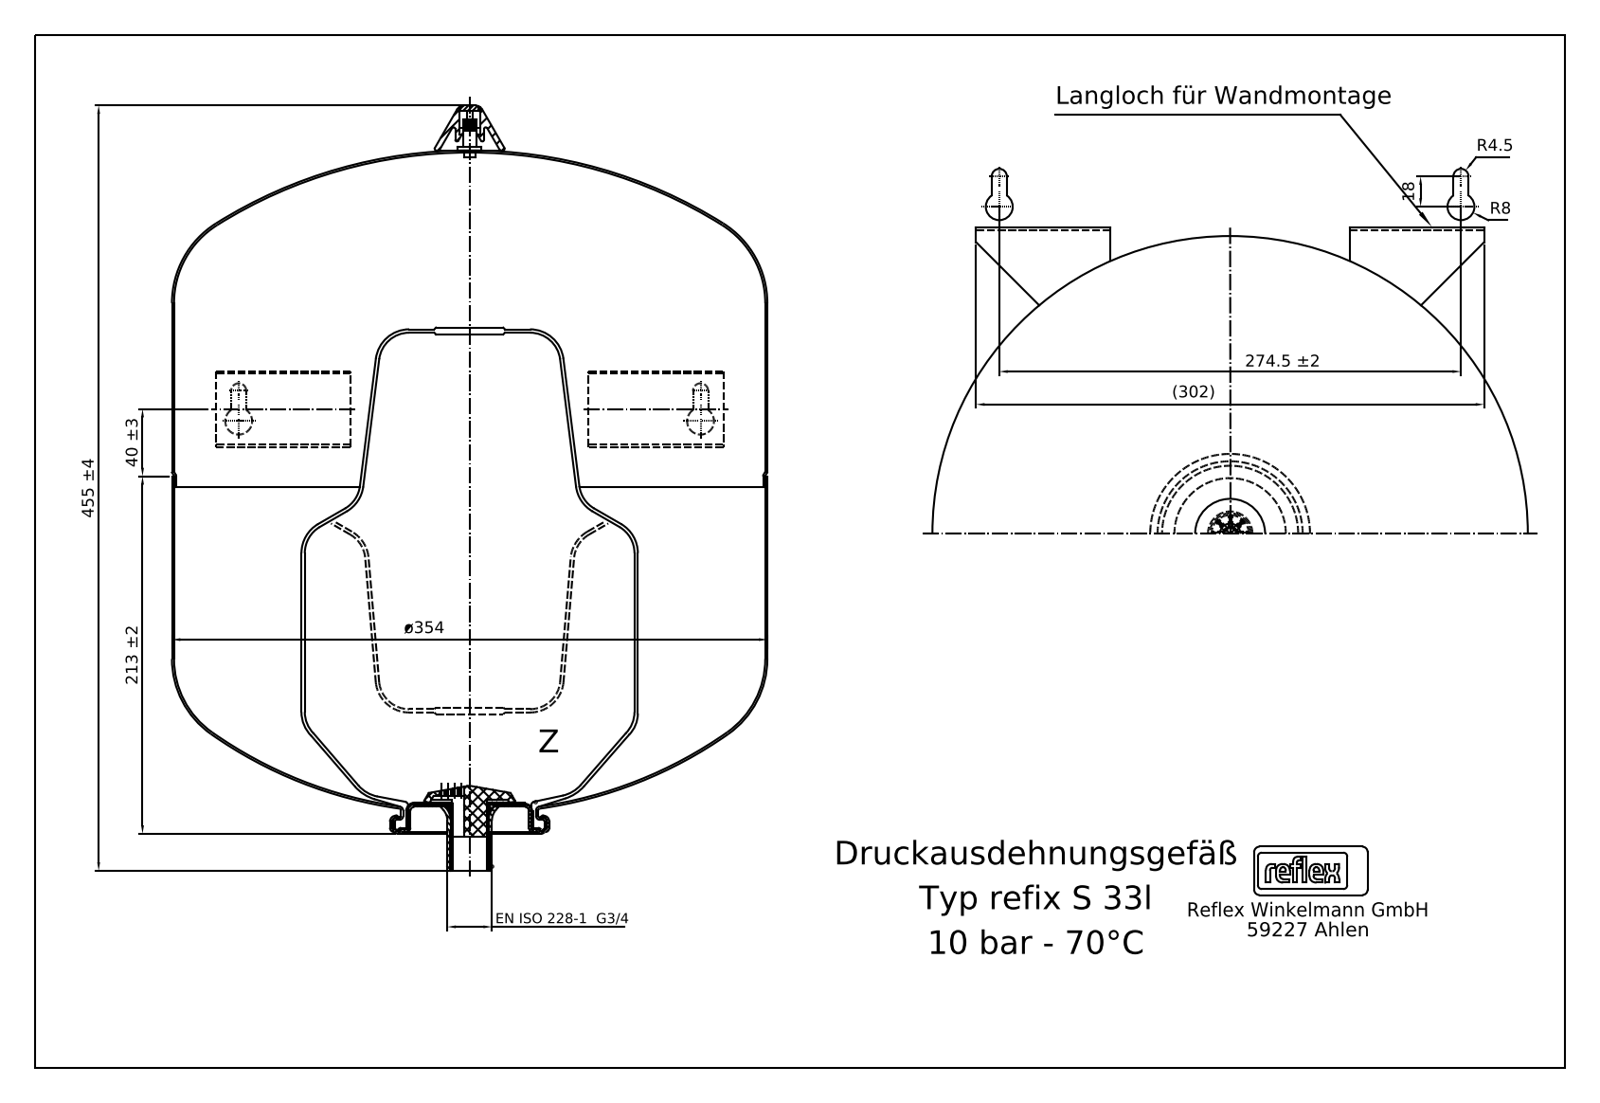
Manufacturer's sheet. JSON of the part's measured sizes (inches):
{"step_written_by": "Mechanical Desktop 2011 (CONFIG_CONTROL_DESIGN)", "units": "inches", "bodies": {"solids": 16, "faces": 276, "planar": 124, "cylindrical": 102, "other": 50}, "overall_size": [17.913, 14.185, 13.937], "volume_in3": 1967, "surface_area_in2": 1512, "round_holes": [[0.555, 1], [0.63, 1], [0.744, 1]], "round_bosses_or_shafts": [[13.937, 1], [3.78, 1], [3.228, 1], [1.059, 1], [0.673, 1], [0.354, 1], [0.236, 1]], "partial_cylinders_radius": [[0.059, 4], [0.088, 4], [0.093, 4], [0.157, 4], [0.159, 4], [0.06, 2], [0.079, 2], [0.088, 2]], "face_to_face_distances": [8.228, 0.079, 11.535, 3.307, 0.512, 3.819, 12.047, 1.693, 8.13, 7.618]}
